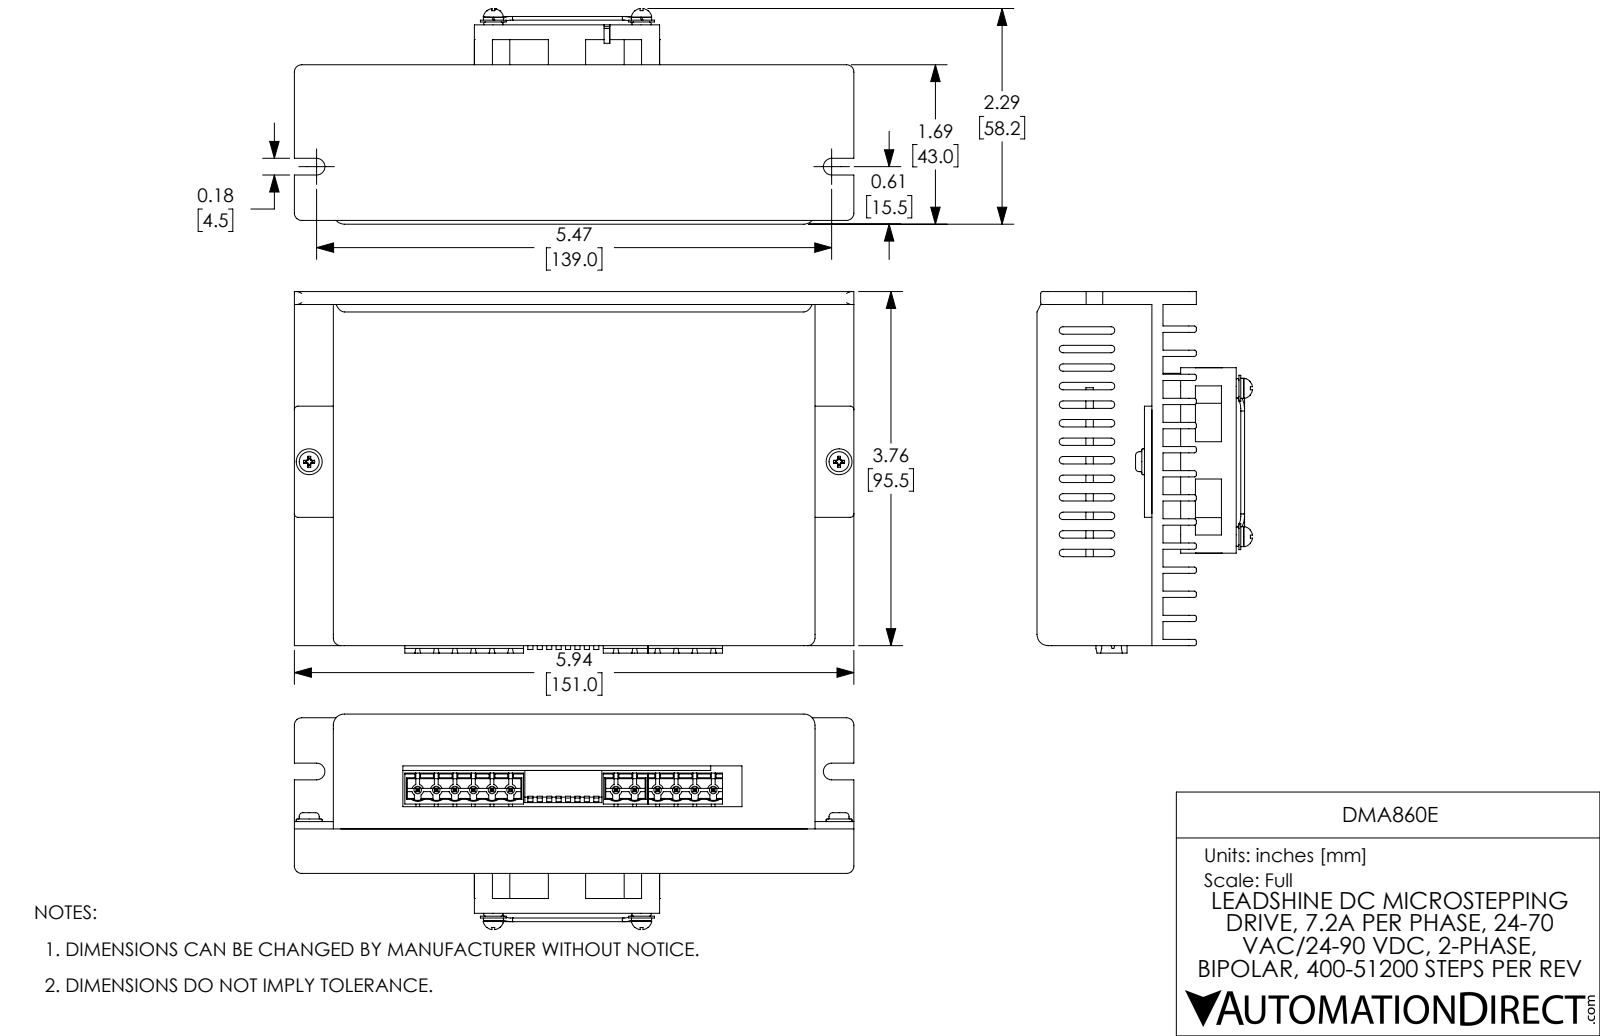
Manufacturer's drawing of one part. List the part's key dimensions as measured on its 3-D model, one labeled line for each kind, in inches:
Part name (STEP PRODUCT): DMA860E_3D CAOMPLETE 3
STEP written by: SolidWorks 2017 (AUTOMOTIVE_DESIGN)
Units: inches
Bodies: 24 solids, 1911 faces (1266 planar, 442 cylindrical, 203 other)
Overall size (bounding box): 5.945 × 3.839 × 2.289
Volume: 11.03 in³ · Surface area: 248.4 in²
Round holes (diameter × count): ⌀0.08 ×12, ⌀0.118 ×4, ⌀0.169 ×4, ⌀0.157 ×2, ⌀1.827 ×1, ⌀1.85 ×1
Round bosses / shafts (diameter × count): ⌀0.039 ×8, ⌀0.276 ×6, ⌀0.213 ×6, ⌀0.118 ×2, ⌀0.093 ×2, ⌀1.851 ×1, ⌀0.984 ×1, ⌀0.787 ×1
Partial cylindrical surfaces — rounded edges, fillets, slot ends (radius × count): R0.02 ×30, R0.039 ×30, R0.061 ×12, R0.11 ×12, R0.031 ×8, R0.062 ×8, R0.079 ×6, R0.063 ×4
Main face-to-face distances: 1.22, 0.118, 0.256, 0.512, 0.079, 0.768, 1.024, 0.701, 1.535, 1.339
Hole centre spacings: 1.575, 0.022, 1.113, 2.227, 0.198, 0.591, 0.197, 0.394
